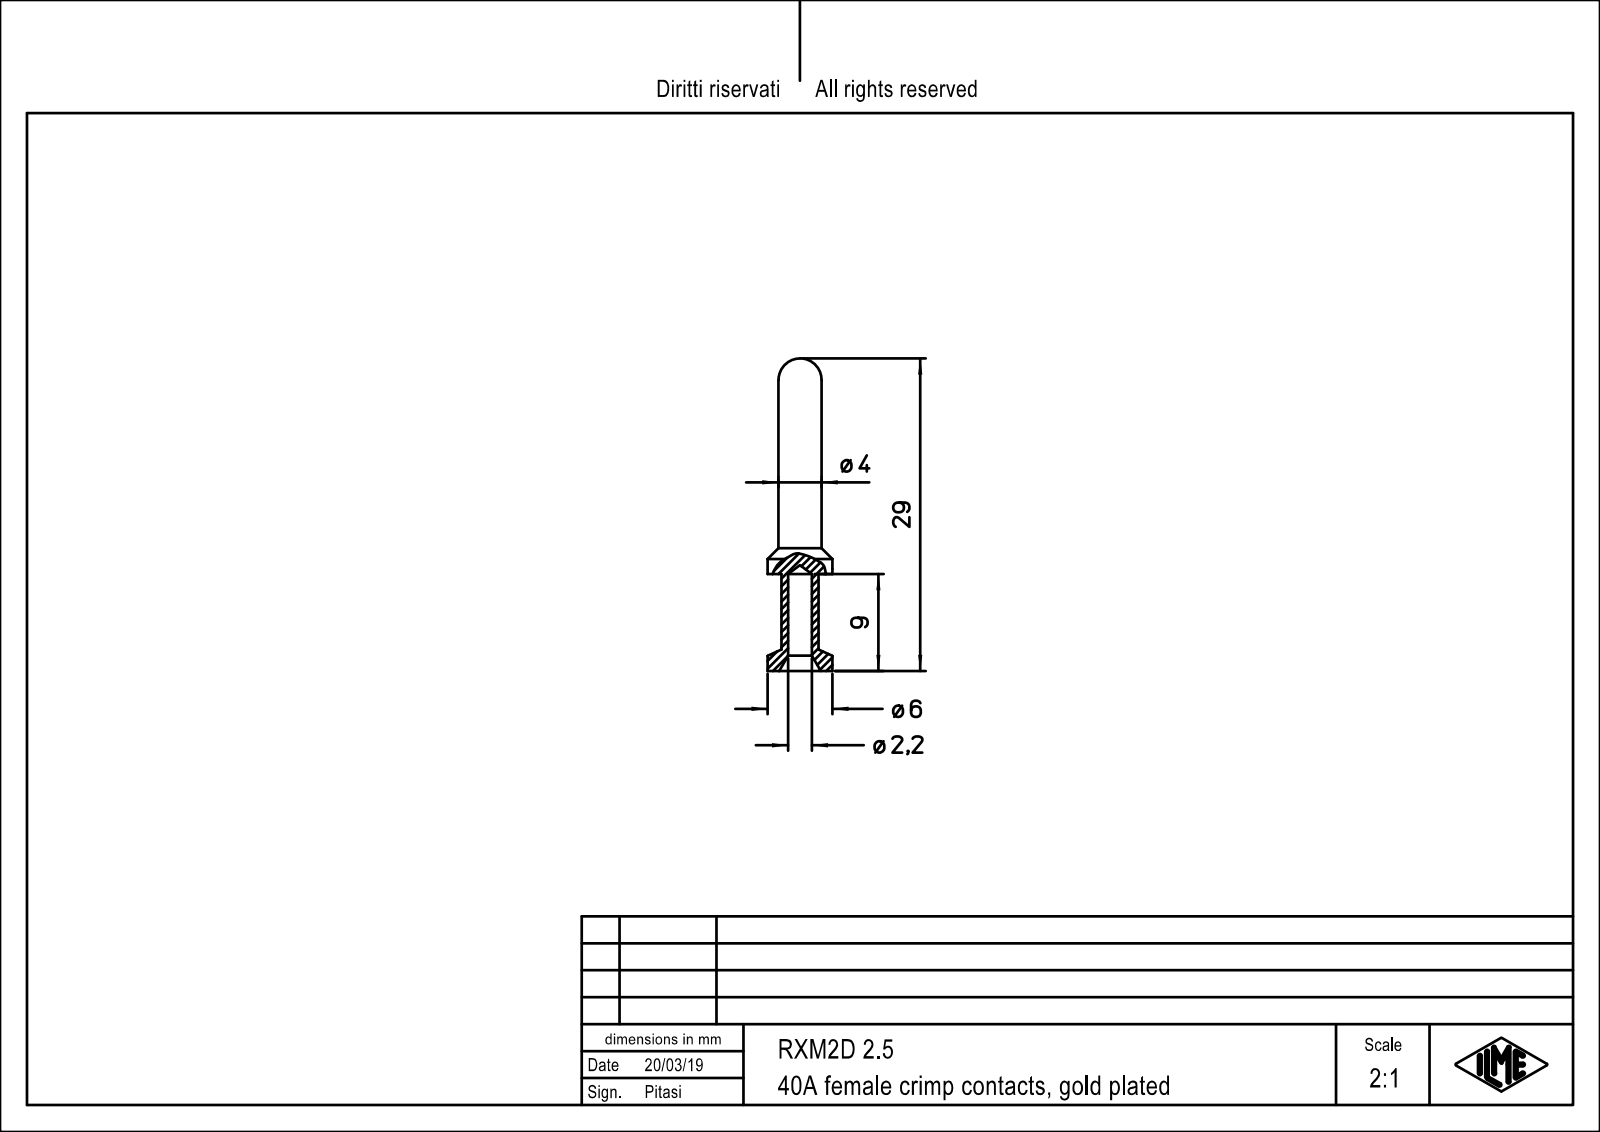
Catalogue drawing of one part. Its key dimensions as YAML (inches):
part_name: "RXM2D_2-5"
step_written_by: "PTC Creo Elements/Direct Modeling 19.0E 27-Jun-2016 (C) Parametric Technology GmbH (AUTOMOTIVE_DESIGN)"
units: inches
bodies: {solids: 1, faces: 25, planar: 3, cylindrical: 12, other: 10}
overall_size: [1.142, 0.236, 0.236]
volume: 0.022
surface_area: 0.772
round_holes:
  - {diameter: 0.087, count: 1}
round_bosses_or_shafts:
  - {diameter: 0.236, count: 1}
  - {diameter: 0.157, count: 1}
  - {diameter: 0.136, count: 1}
face_to_face_distances: [0.354, 0.315, 0.039]
